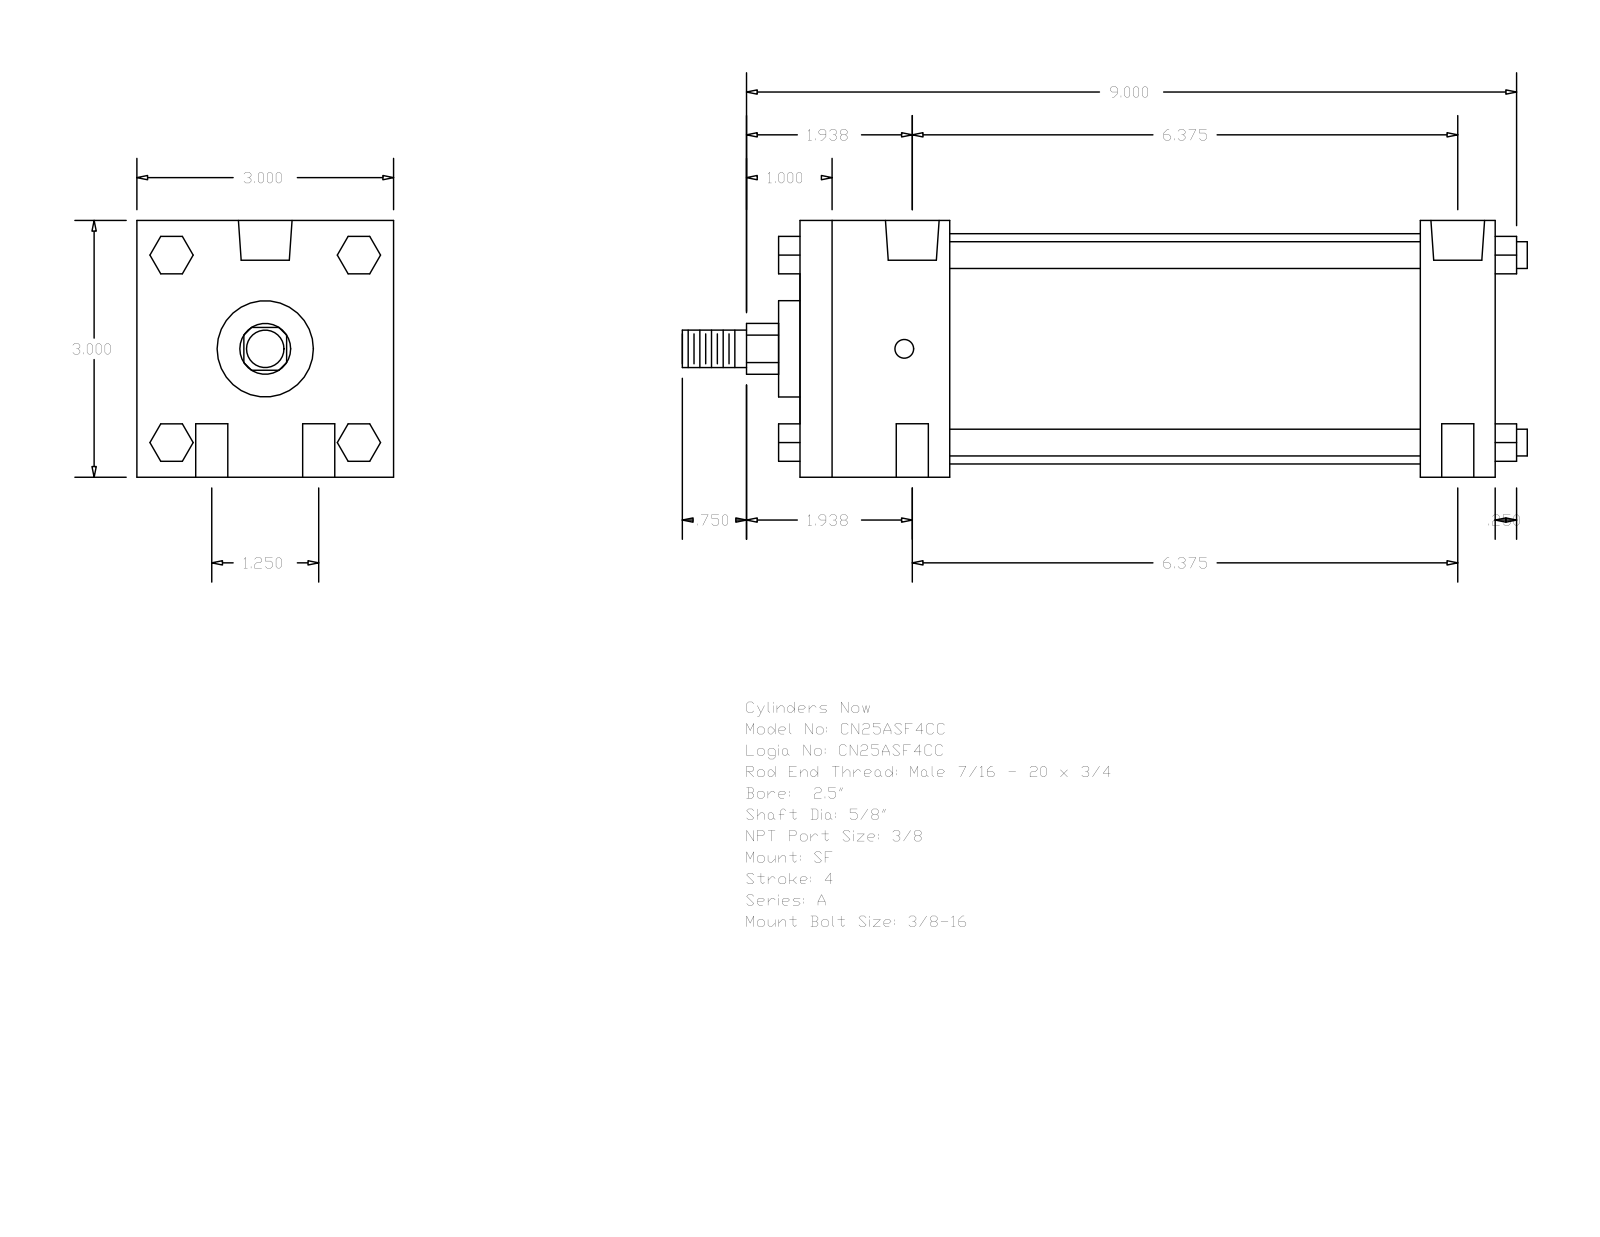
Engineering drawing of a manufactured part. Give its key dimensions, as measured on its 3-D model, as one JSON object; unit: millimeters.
{"part_name": "A_SF__0250_0.625", "step_written_by": "GSSL Pune (CONFIG_CONTROL_DESIGN)", "units": "millimeters", "bodies": {"solids": 0, "faces": 124, "planar": 94, "cylindrical": 30, "other": 0}, "overall_size": [250.82, 76.2, 76.2], "round_holes": [[9.53, 4], [5.56, 2], [15.93, 2]], "round_bosses_or_shafts": [[7.94, 4], [68.33, 1], [28.57, 1], [15.88, 1], [11.11, 1]], "partial_cylinders_radius": [[7.54, 1]], "face_to_face_distances": [76.2, 206.37, 44.45, 184.15, 22.22, 139.7, 161.92, 6.35, 212.72, 50.8], "hole_center_spacings": [15.88, 162.71, 161.93, 31.76, 165.02, 166.69]}
